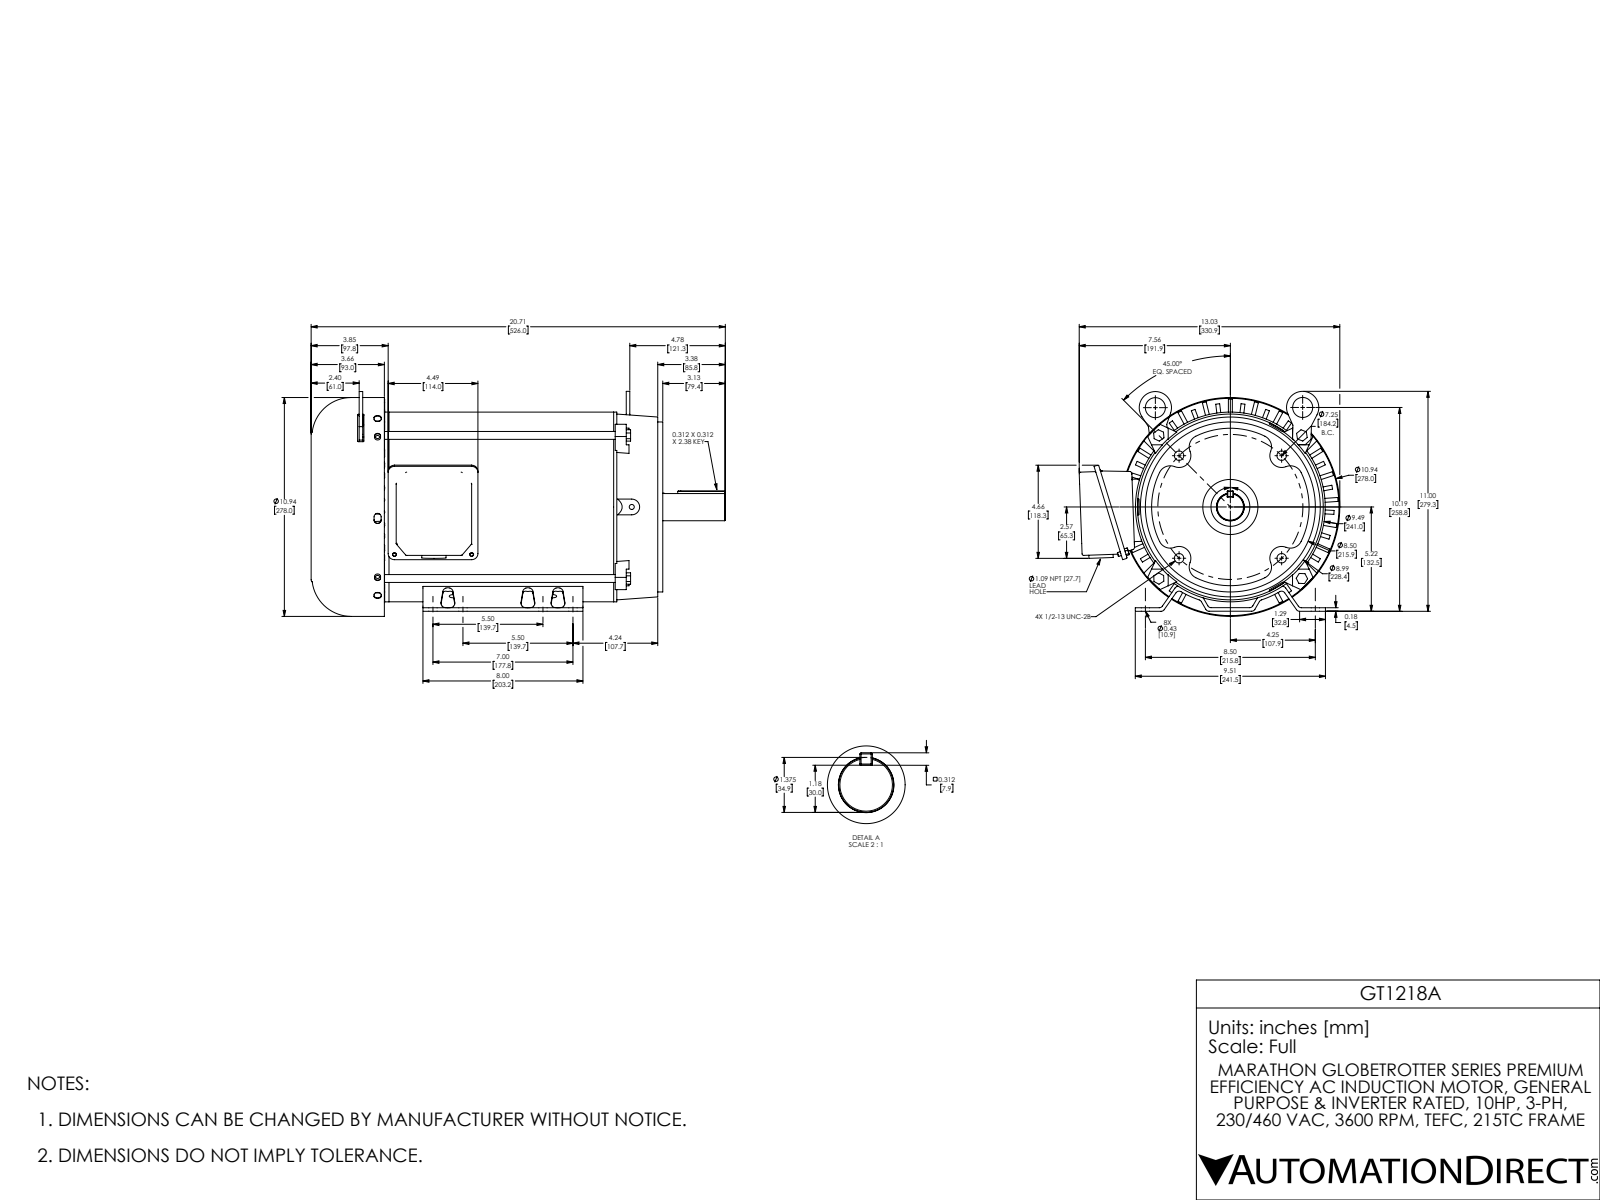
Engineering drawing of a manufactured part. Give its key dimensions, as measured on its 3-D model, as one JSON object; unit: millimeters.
{"part_name": "SS620688-215TC r1 Good Coord", "step_written_by": "SolidWorks 2017 (AUTOMOTIVE_DESIGN)", "units": "millimeters", "bodies": {"solids": 17, "faces": 2005, "planar": 1190, "cylindrical": 593, "other": 222}, "overall_size": [526, 330.9, 285.9], "volume_mm3": 4426000, "surface_area_mm2": 1440000, "round_holes": [[9.4, 10], [10.5, 8], [8, 5], [5.1, 4], [6.4, 4], [9, 4], [12, 4], [5.5, 3], [8.5, 2], [12.7, 2], [25.5, 2], [25, 1]], "round_bosses_or_shafts": [[10, 4], [5, 2], [278, 1], [241, 1], [240.9, 1], [237, 1], [235.5, 1], [215.9, 1]], "partial_cylinders_radius": [[1.5, 53], [2.5, 36], [1.8, 35], [2, 16], [3, 16], [4.8, 16], [1, 12], [4.5, 12]], "face_to_face_distances": [4.5, 6, 384, 390.6, 6.6, 378, 384.6, 25.4, 31.4, 409.4], "hole_center_spacings": [158.1, 25.4, 36.4, 38.1, 39.8, 63.5, 88.9, 130.3]}
